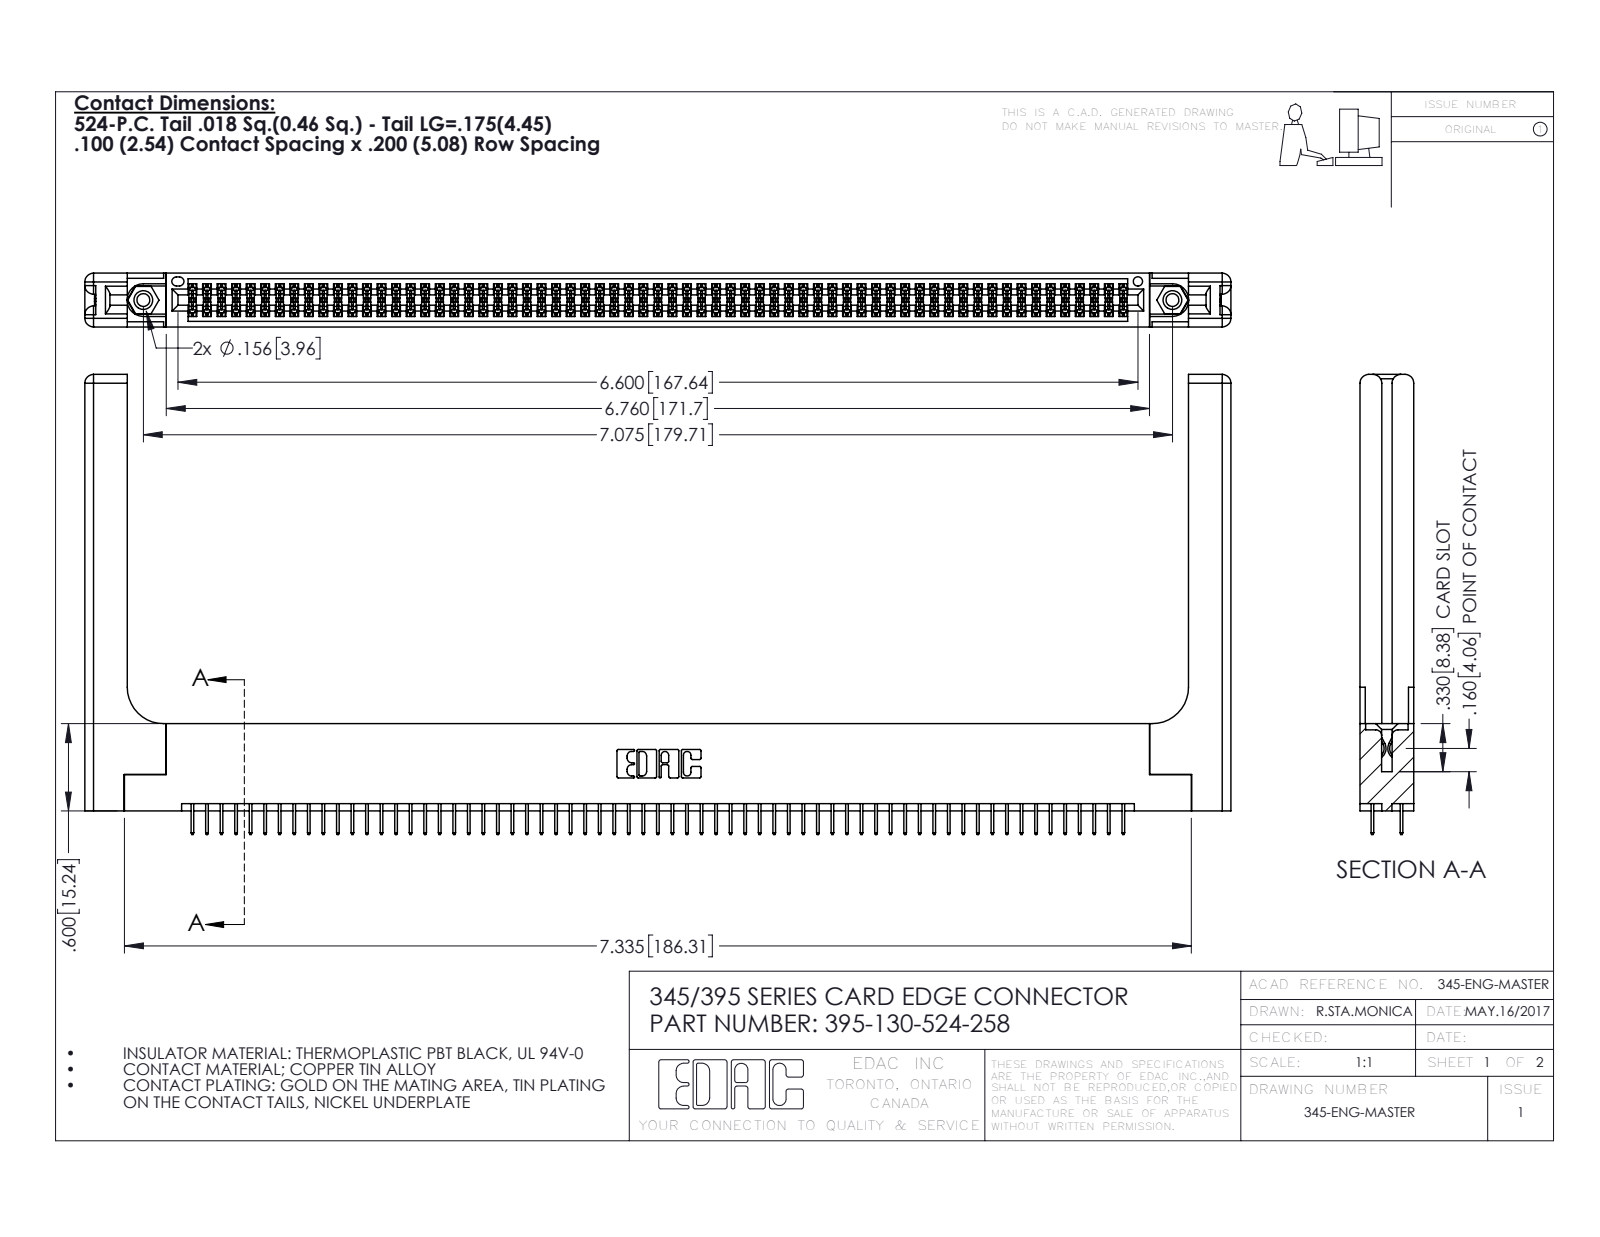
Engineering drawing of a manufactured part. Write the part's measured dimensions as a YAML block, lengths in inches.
part_name: "345-292-001_345-293-124; 345-220-058_345-220-058; 395-130-524-258; 345-250-001_345-250-001-102 (+1 more)"
step_written_by: "SolidWorks 2016 (CONFIG_CONTROL_DESIGN)"
units: inches
bodies: {solids: 135, faces: 7402, planar: 5298, cylindrical: 2044, other: 60}
overall_size: [7.879, 3.162, 0.37]
volume: 1.705
surface_area: 52.31
round_holes:
  - {diameter: 0.089, count: 2}
  - {diameter: 0.125, count: 2}
  - {diameter: 0.156, count: 2}
  - {diameter: 0.064, count: 1}
round_bosses_or_shafts:
  - {diameter: 0.155, count: 2}
partial_cylinders:
  - {radius: 0.006, count: 195}
  - {radius: 0.01, count: 22}
  - {radius: 0.06, count: 16}
  - {radius: 0.007, count: 6}
  - {radius: 0.031, count: 6}
  - {radius: 0.026, count: 3}
  - {radius: 0.014, count: 2}
  - {radius: 0.019, count: 2}
face_to_face_distances: [0.072, 0.298, 0.37, 0.2, 0.098, 0.272, 0.025, 0.225, 0.072, 0.148]
hole_center_spacings: [0.27, 6.839, 7.075]
